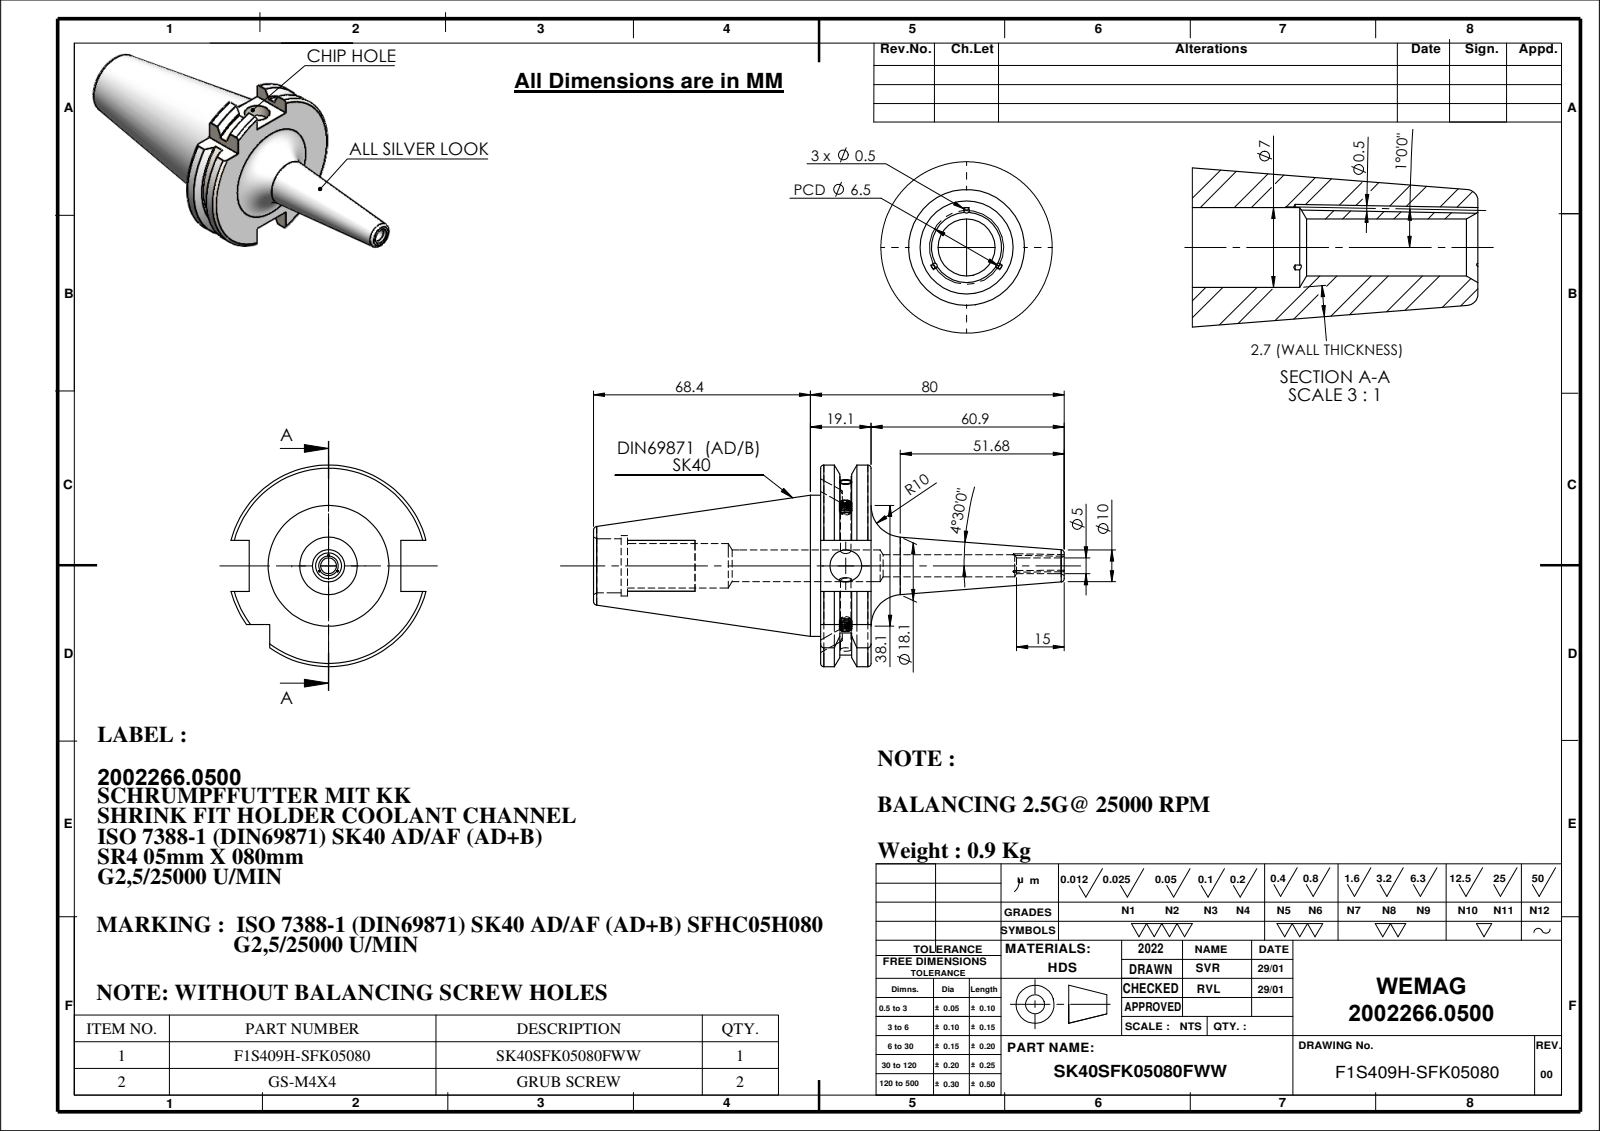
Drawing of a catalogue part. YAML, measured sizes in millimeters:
part_name: "GS-M4X4_DIN 913 - M4 x 4-N; SK40SFK05080FWW; 91406-SR405080"
step_written_by: "SolidWorks 2018 (CONFIG_CONTROL_DESIGN)"
units: millimeters
bodies: {solids: 3, faces: 206, planar: 46, cylindrical: 58, other: 102}
overall_size: [148.4, 63.55, 61.48]
volume: 111621
surface_area: 24918
round_holes:
  - {diameter: 0.5, count: 3}
  - {diameter: 10, count: 2}
  - {diameter: 3.3, count: 1}
  - {diameter: 4.99, count: 1}
  - {diameter: 7, count: 1}
  - {diameter: 14, count: 1}
  - {diameter: 17, count: 1}
  - {diameter: 19, count: 1}
round_bosses_or_shafts:
  - {diameter: 4, count: 2}
  - {diameter: 44.45, count: 1}
partial_cylinders:
  - {radius: 28.12, count: 1}
  - {radius: 31.77, count: 1}
face_to_face_distances: [15.9, 16.1, 47.8, 60.9, 76.8, 71.6, 87.5, 10.7, 77.63, 66.93]
